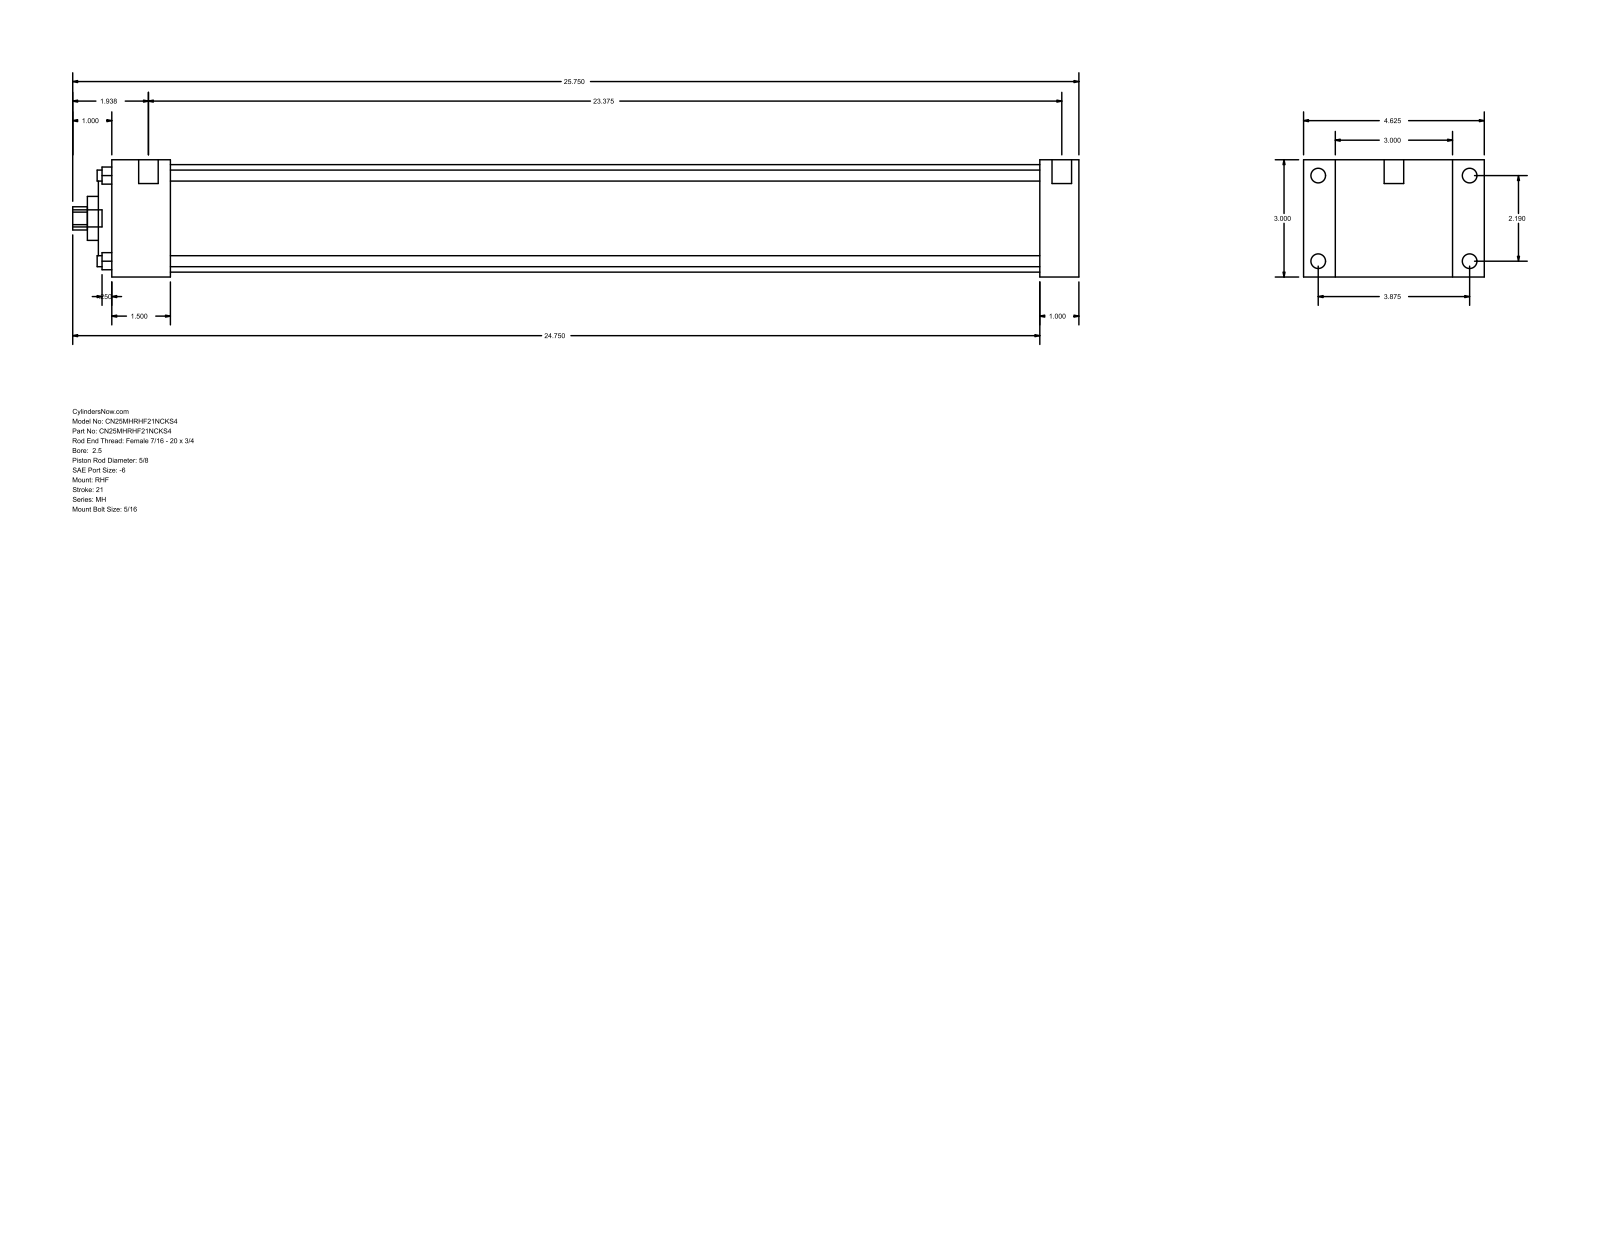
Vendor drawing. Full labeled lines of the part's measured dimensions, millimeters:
Part name (STEP PRODUCT): MH_RHF__0250_0.625
STEP written by: GSSL Pune (CONFIG_CONTROL_DESIGN)
Units: millimetres
Bodies: 0 solids, 90 faces (61 planar, 29 cylindrical, 0 other)
Overall size (bounding box): 654.05 × 117.47 × 76.2
Round holes (diameter × count): ⌀7.14 ×4, ⌀15.88 ×1, ⌀28.57 ×1, ⌀55.55 ×1, ⌀69.85 ×1
Round bosses / shafts (diameter × count): ⌀9.53 ×4, ⌀5.56 ×4, ⌀12.7 ×2, ⌀11.11 ×1
Partial cylindrical surfaces — rounded edges, fillets, slot ends (radius × count): R7.54 ×1
Main face-to-face distances: 76.2, 25.4, 20.64, 96.84, 628.65, 603.25, 117.48, 38.1, 565.15, 590.55
Hole centre spacings: 39.33, 55.62, 78.66
